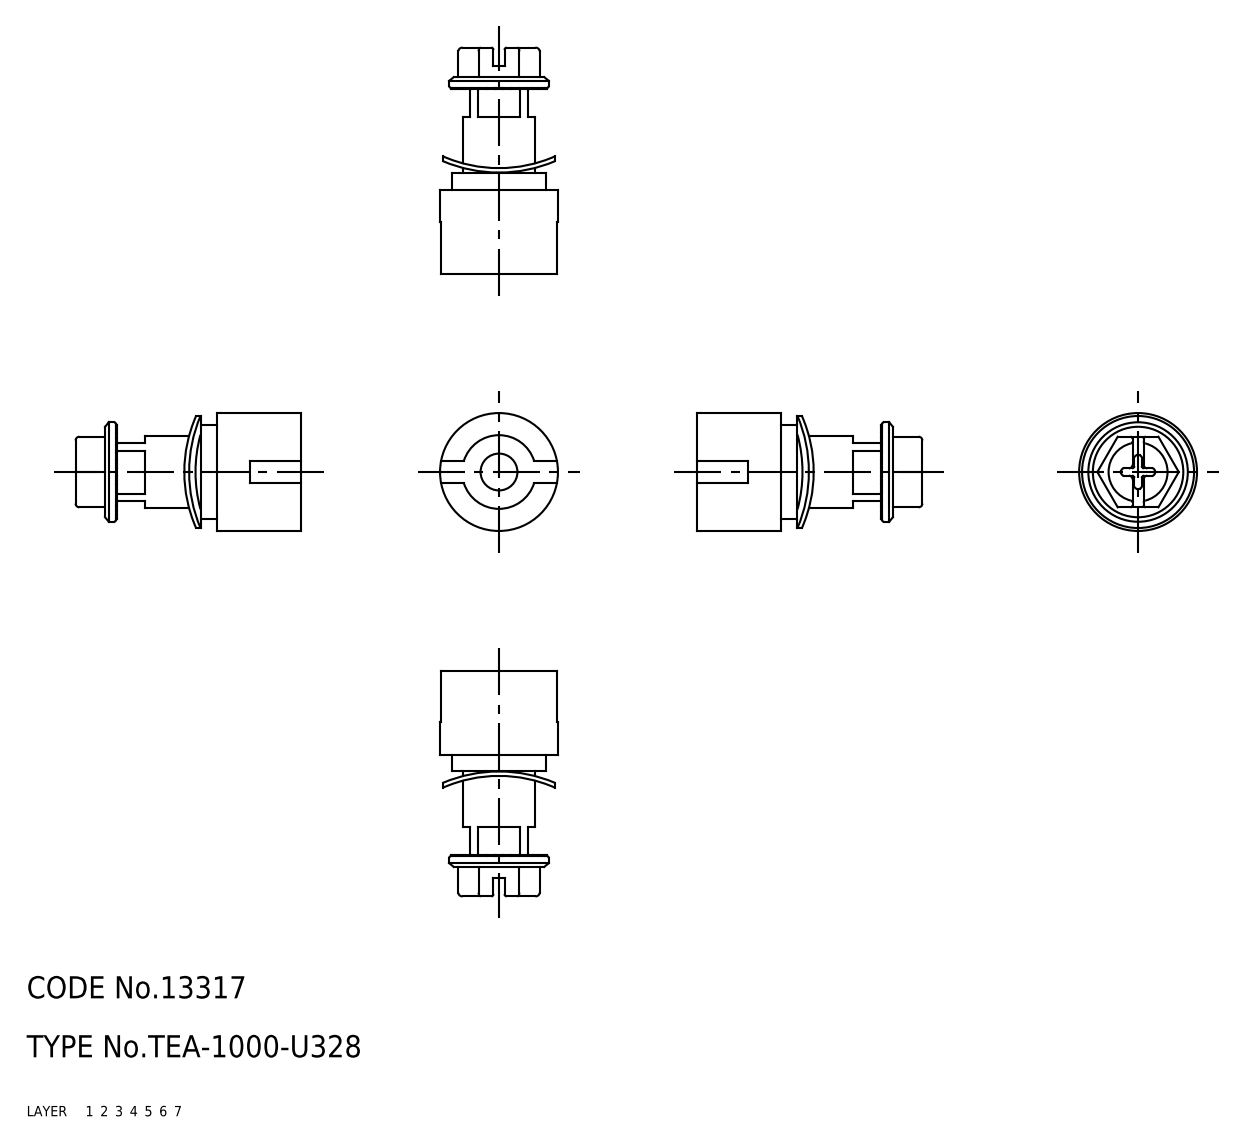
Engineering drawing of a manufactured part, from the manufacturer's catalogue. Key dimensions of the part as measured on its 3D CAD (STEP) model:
Part name (STEP PRODUCT): shaft
STEP written by: CADfix (AUTOMOTIVE_DESIGN)
Units: millimetres
Bodies: 1 solid, 144 faces (0 planar, 0 cylindrical, 144 other)
Overall size (bounding box): 30.95 × 16 × 16
Volume: 3 413 mm³ · Surface area: 2 448 mm²
